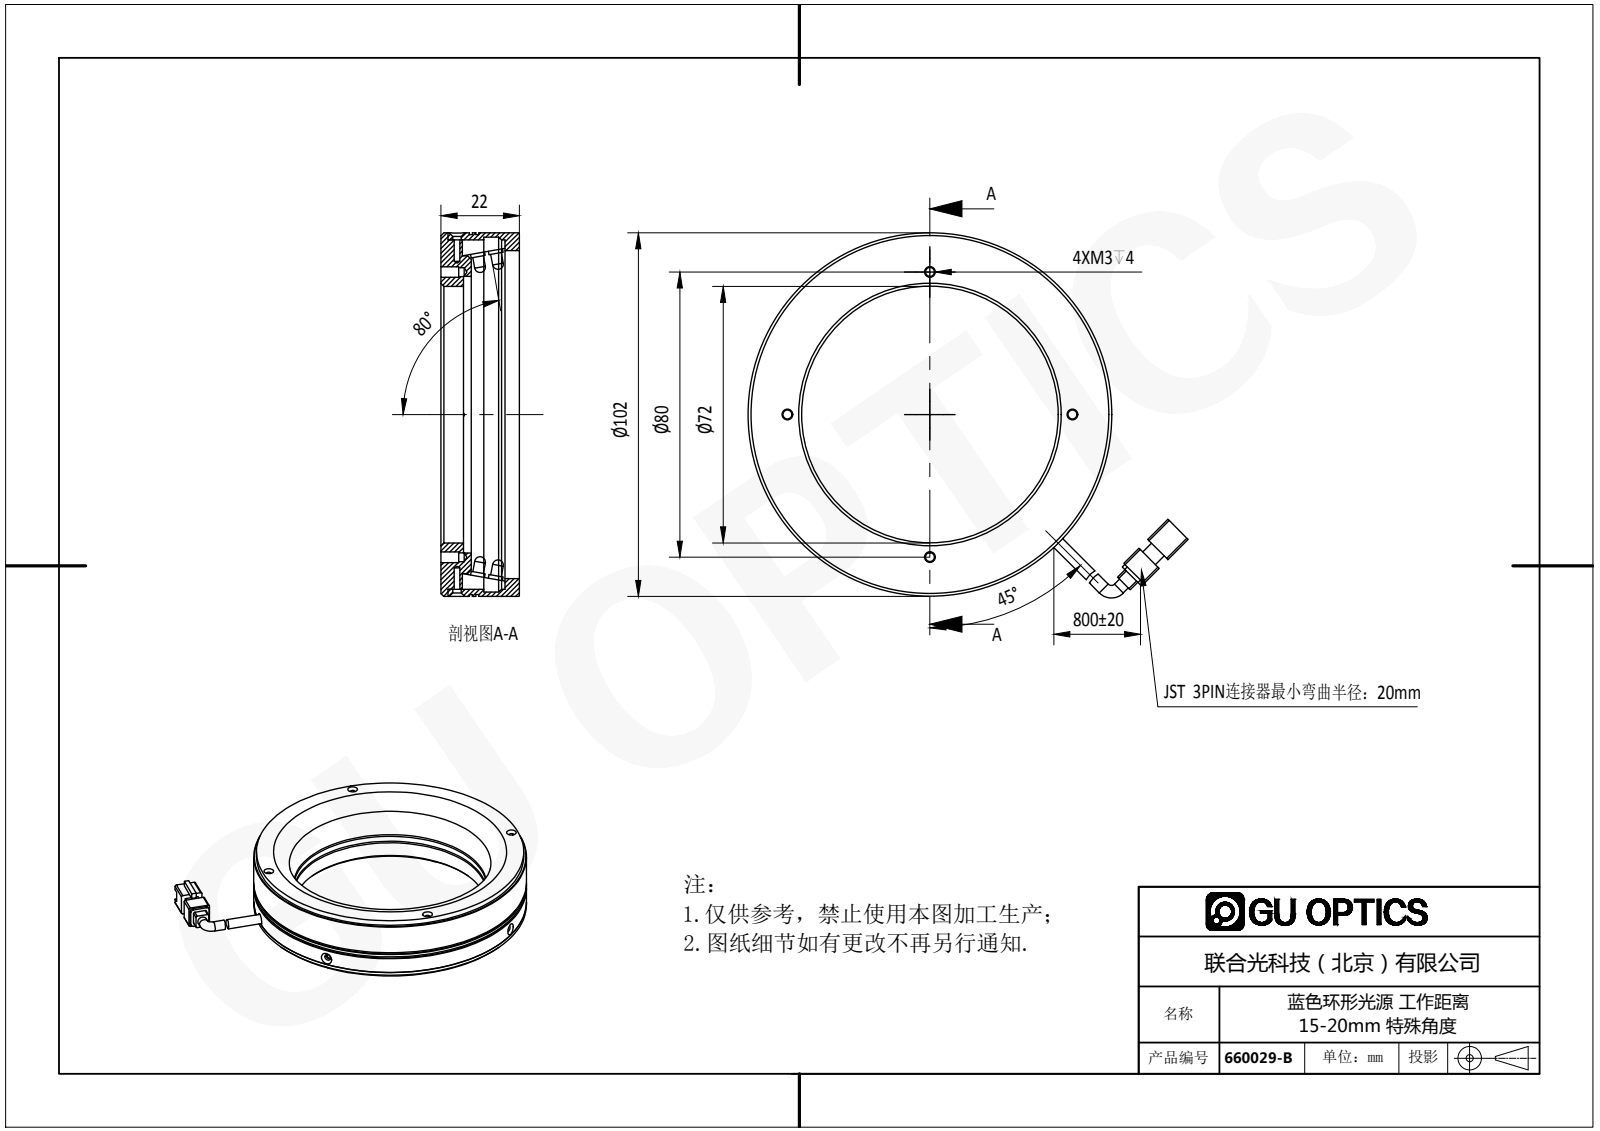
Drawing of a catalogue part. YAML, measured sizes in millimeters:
part_name: "660029-B"
step_written_by: "SolidWorks 2016 (AUTOMOTIVE_DESIGN)"
units: millimeters
bodies: {solids: 111, faces: 2068, planar: 1343, cylindrical: 545, other: 180}
overall_size: [123.48, 102.42, 24.3]
volume: 59477
surface_area: 60227
round_holes:
  - {diameter: 1.25, count: 4}
  - {diameter: 1.7, count: 4}
  - {diameter: 2.5, count: 4}
  - {diameter: 3, count: 4}
  - {diameter: 1.6, count: 2}
  - {diameter: 2.4, count: 2}
  - {diameter: 3.5, count: 2}
  - {diameter: 72, count: 1}
  - {diameter: 77.6, count: 1}
  - {diameter: 92, count: 1}
  - {diameter: 98, count: 1}
  - {diameter: 99.6, count: 1}
round_bosses_or_shafts:
  - {diameter: 3.8, count: 105}
  - {diameter: 3, count: 105}
  - {diameter: 3.5, count: 2}
  - {diameter: 102, count: 1}
  - {diameter: 101, count: 1}
  - {diameter: 100, count: 1}
  - {diameter: 89.11, count: 1}
  - {diameter: 76, count: 1}
partial_cylinders:
  - {radius: 0.5, count: 8}
  - {radius: 1, count: 4}
  - {radius: 1.6, count: 1}
  - {radius: 7, count: 1}
face_to_face_distances: [22, 2, 6, 4, 16, 18, 24, 2.5, 12, 1]
hole_center_spacings: [34.2, 80.89, 40, 47.5, 56.57, 67.18, 80, 95.01]
